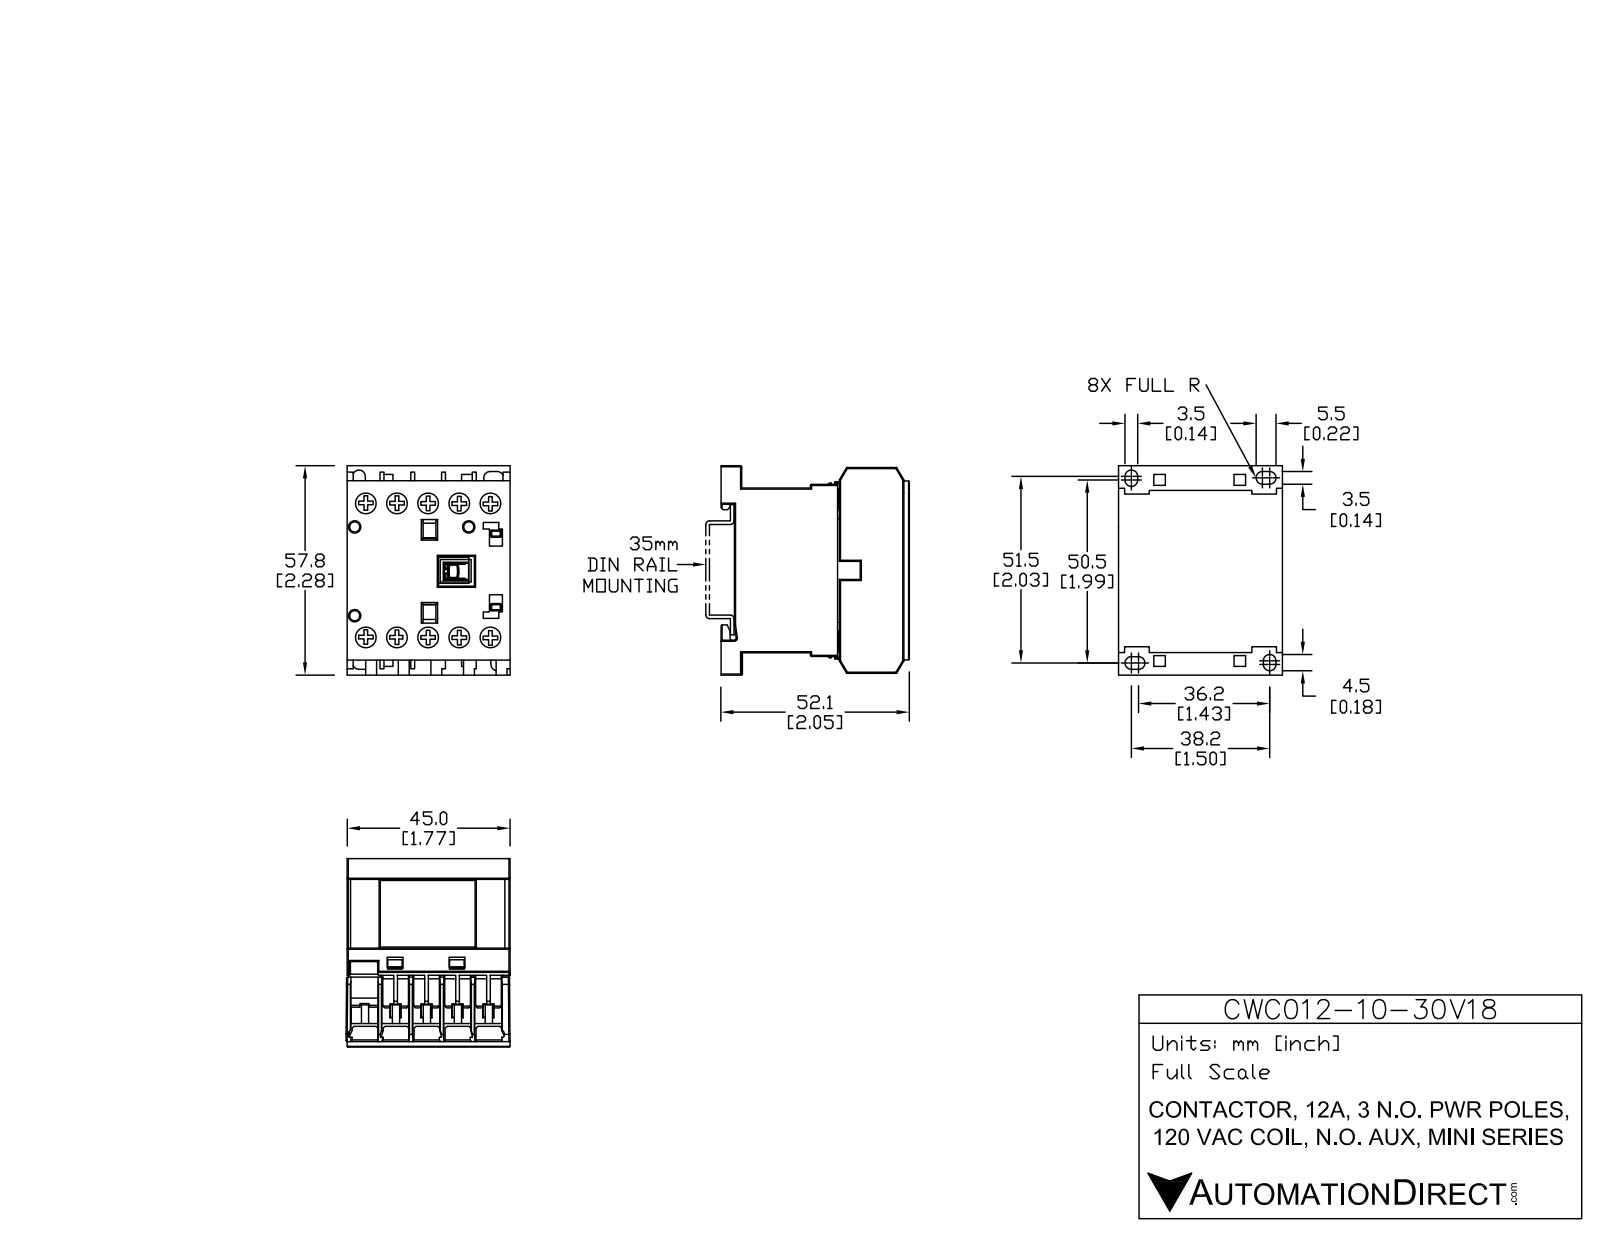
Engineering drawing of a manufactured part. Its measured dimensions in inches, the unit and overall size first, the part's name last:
Units: inches
Overall size (bounding box): 2.285 × 2.052 × 1.801
Round holes (diameter × count): ⌀0.244 ×10, ⌀0.11 ×3
Round bosses / shafts (diameter × count): ⌀0.232 ×10
Partial cylindrical surfaces — rounded edges, fillets, slot ends (radius × count): R0.012 ×20, R0.068 ×6, R0.068 ×2, R0.013 ×1, R0.017 ×1, R0.022 ×1
Main face-to-face distances: 0.325, 1.791, 0.049, 0.65, 0.374, 0.217, 0.699, 0.202, 0.419, 0.276
Hole centre spacings: 0.337, 1.494, 0.673, 1.603, 1.455, 1.01, 1.771, 0.272
Volume: 5.927 in³ · Surface area: 47.18 in²
Bodies: 15 solids, 535 faces (445 planar, 90 cylindrical, 0 other)
Part name (STEP PRODUCT): CWC12-10-30V18
STEP written by: SolidWorks 2013 (AUTOMOTIVE_DESIGN)
